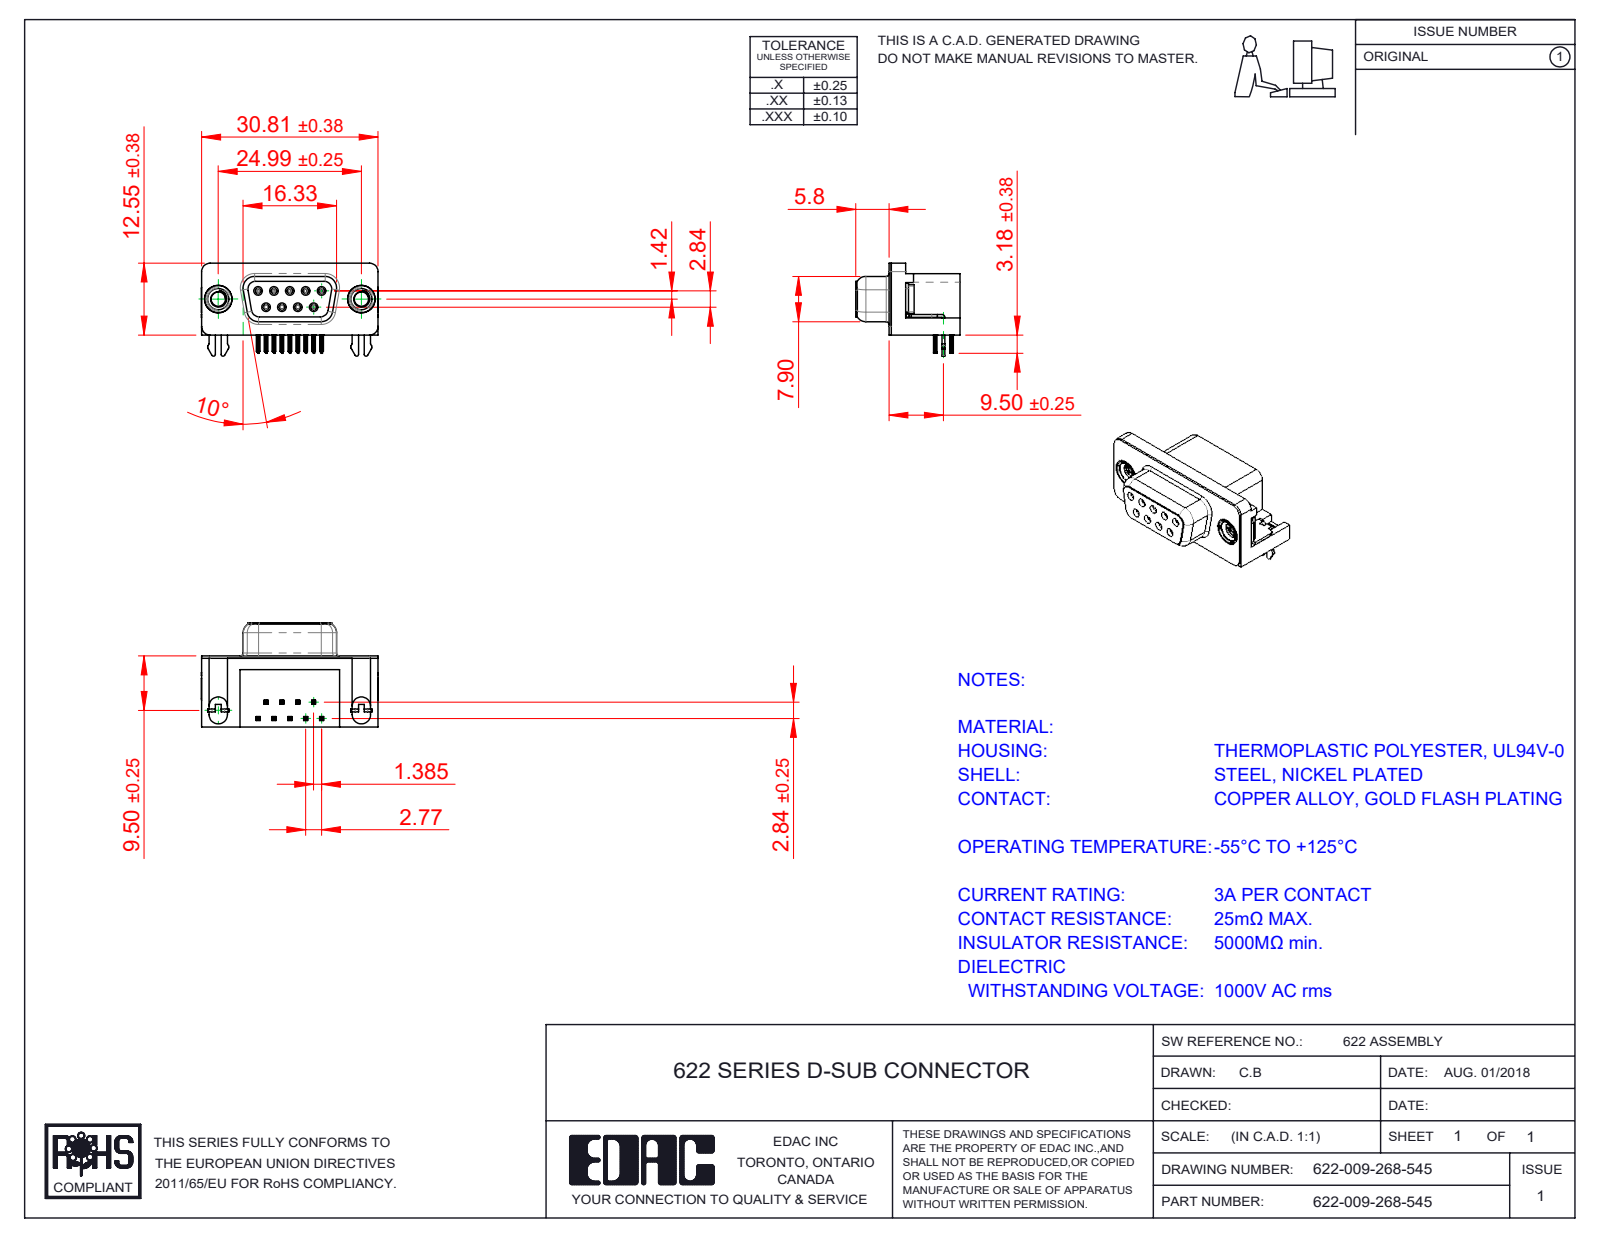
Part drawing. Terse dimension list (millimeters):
name: 622 Socket Bottom; 622 M3 Threaded Rivet; 622 Housing_9 Socket; 622 Contact Top (+3 more)
written by: SolidWorks 2016 (CONFIG_CONTROL_DESIGN)
unit: mm
bodies: 15 solids, 1692 faces (726 planar, 426 cylindrical, 540 other)
size: 30.89 × 18.2 × 16.25
volume: 3 730 mm³; area: 5 151 mm²
holes: 9× ⌀0.8, 9× ⌀0.9, 2× ⌀2, 2× ⌀2.5, 2× ⌀4, 2× ⌀4.8, 2× ⌀5
bosses: 9× ⌀1.2, 2× ⌀4.9, 2× ⌀4.75, 2× ⌀3.9, 2× ⌀3
rounds: 72× R0.1, 36× R0.15, 18× R0.35, 18× R1, 12× R0.25, 9× R0.34, 8× R1.35, 8× R1.6
face distances: 0.4, 12, 12.4, 0.35, 2.9, 2.5, 6.2, 10.34, 9.5, 5.8
hole spacings: 3.16, 2.77, 5.54, 5.03, 5.04, 8.31, 7.48, 7.49
